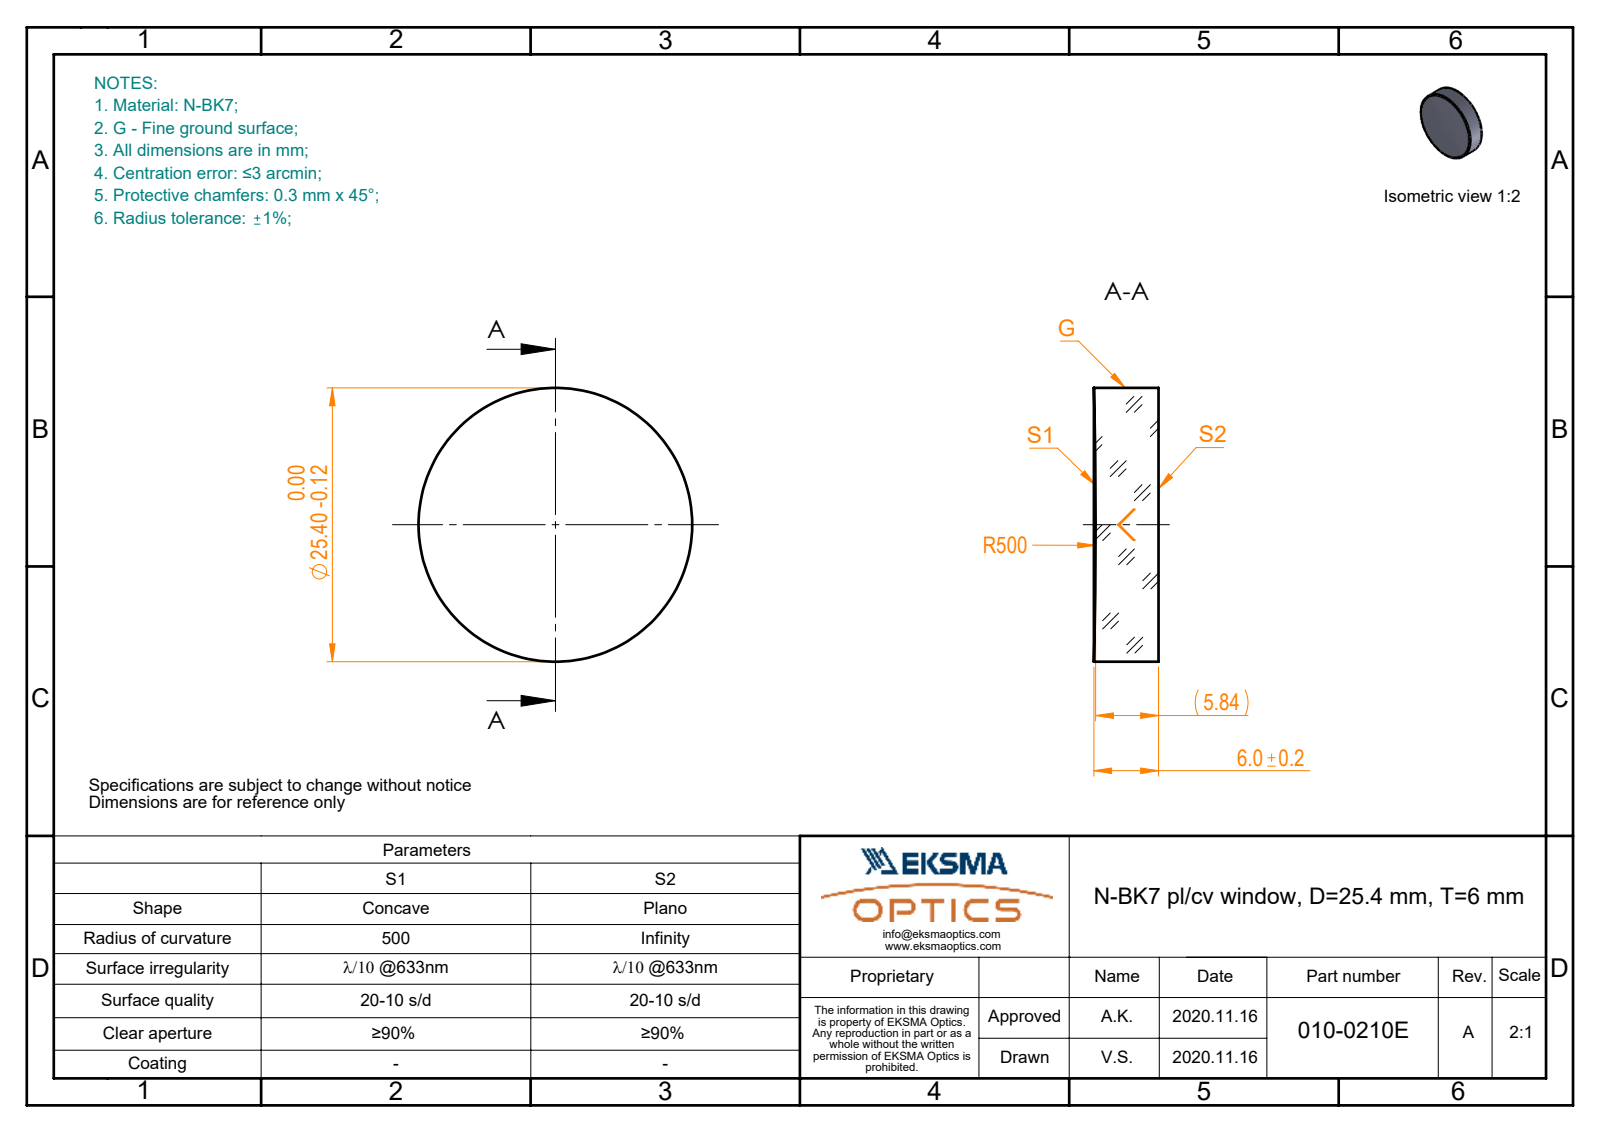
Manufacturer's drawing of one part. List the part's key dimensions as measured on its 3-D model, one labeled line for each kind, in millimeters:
Part name (STEP PRODUCT): 010-0210E_N-BK7_PCV_window
STEP written by: SolidWorks 2019 (CONFIG_CONTROL_DESIGN)
Units: millimetres
Bodies: 1 solid, 5 faces (1 planar, 2 cylindrical, 2 other)
Overall size (bounding box): 25.4 × 25.4 × 6
Volume: 2 999 mm³ · Surface area: 1 492 mm²
Round bosses / shafts (diameter × count): ⌀25.4 ×1
